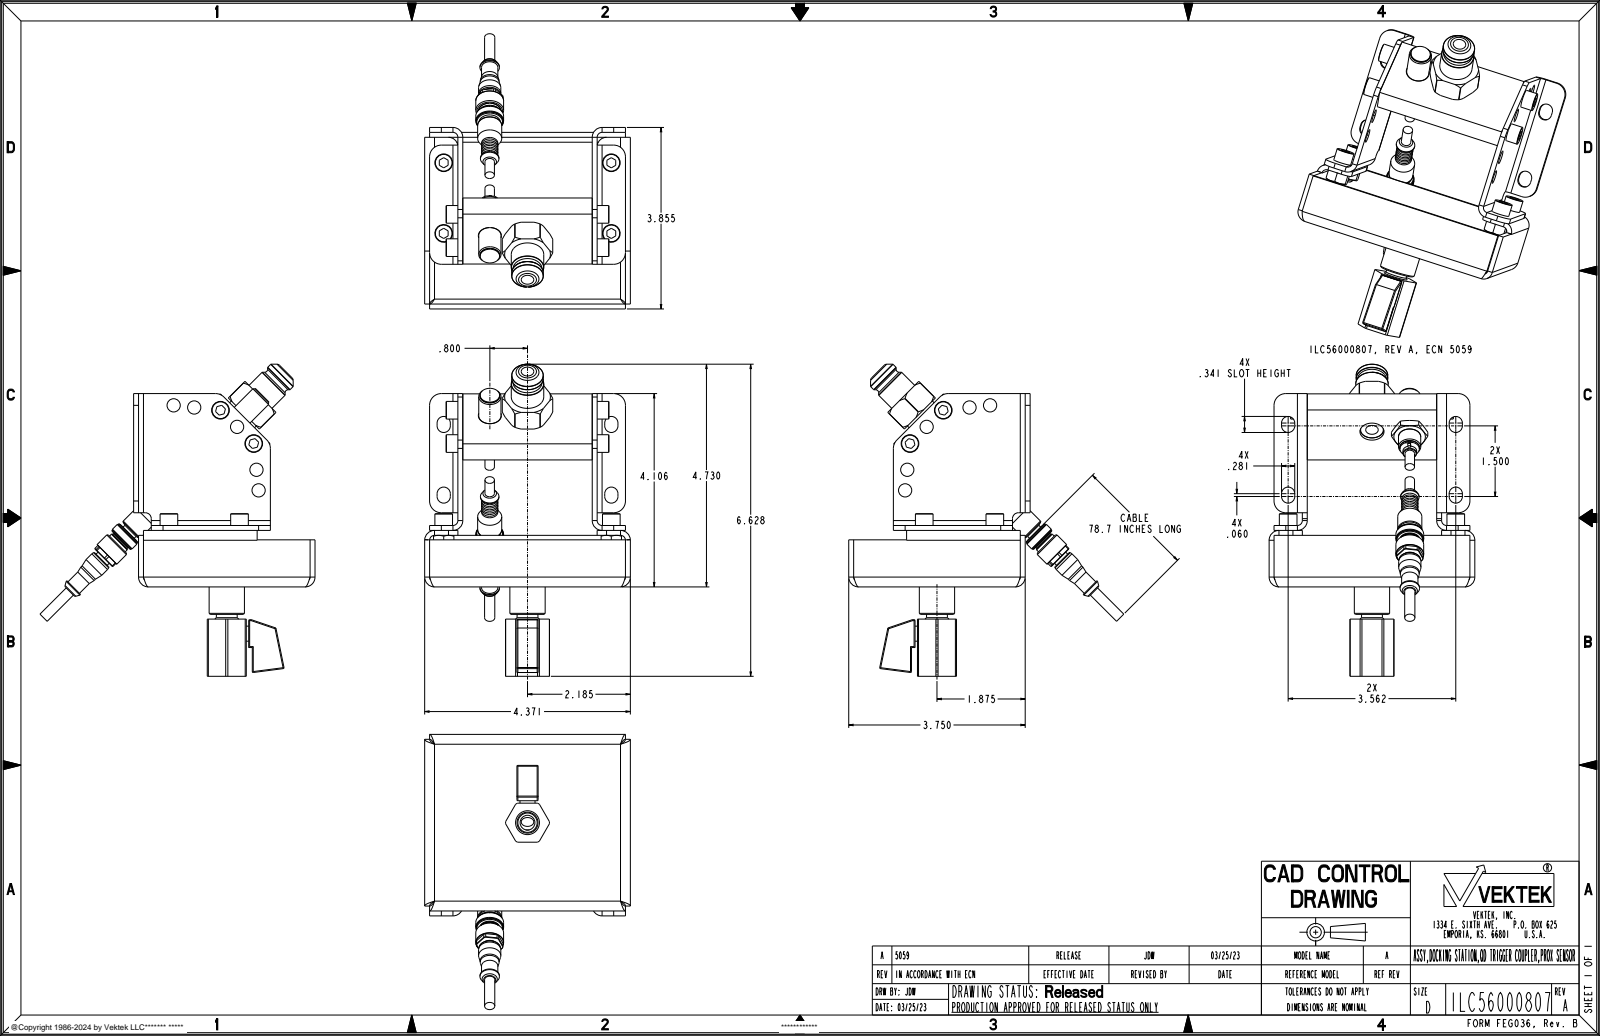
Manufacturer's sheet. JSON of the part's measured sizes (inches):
{"part_name": "ILC56000807", "step_written_by": "CREO PARAMETRIC BY PTC INC, 2021164 (AUTOMOTIVE_DESIGN)", "units": "inches", "bodies": {"solids": 3, "faces": 714, "planar": 279, "cylindrical": 224, "other": 211}, "overall_size": [6.628, 5.845, 4.371], "volume_in3": 10.21, "surface_area_in2": 151.6, "round_holes": [[0.281, 7], [0.266, 1], [0.315, 1], [0.443, 1], [0.511, 1], [0.781, 1]], "round_bosses_or_shafts": [[0.375, 6], [0.346, 4], [0.25, 4], [0.413, 3], [0.236, 3], [0.75, 2], [0.591, 2], [0.571, 2]], "partial_cylinders_radius": [[0.02, 18], [0.105, 10], [0.209, 10], [0.25, 10], [0.141, 8], [0.2, 4], [0.125, 1], [0.283, 1]], "face_to_face_distances": [0.105, 2.855, 0.706, 3.561, 0.104, 3.645, 2.75, 2.96, 0.601, 3.456], "hole_center_spacings": [1, 0.439, 0.5, 0.561, 1.423, 1.478, 1.885, 2.229]}
